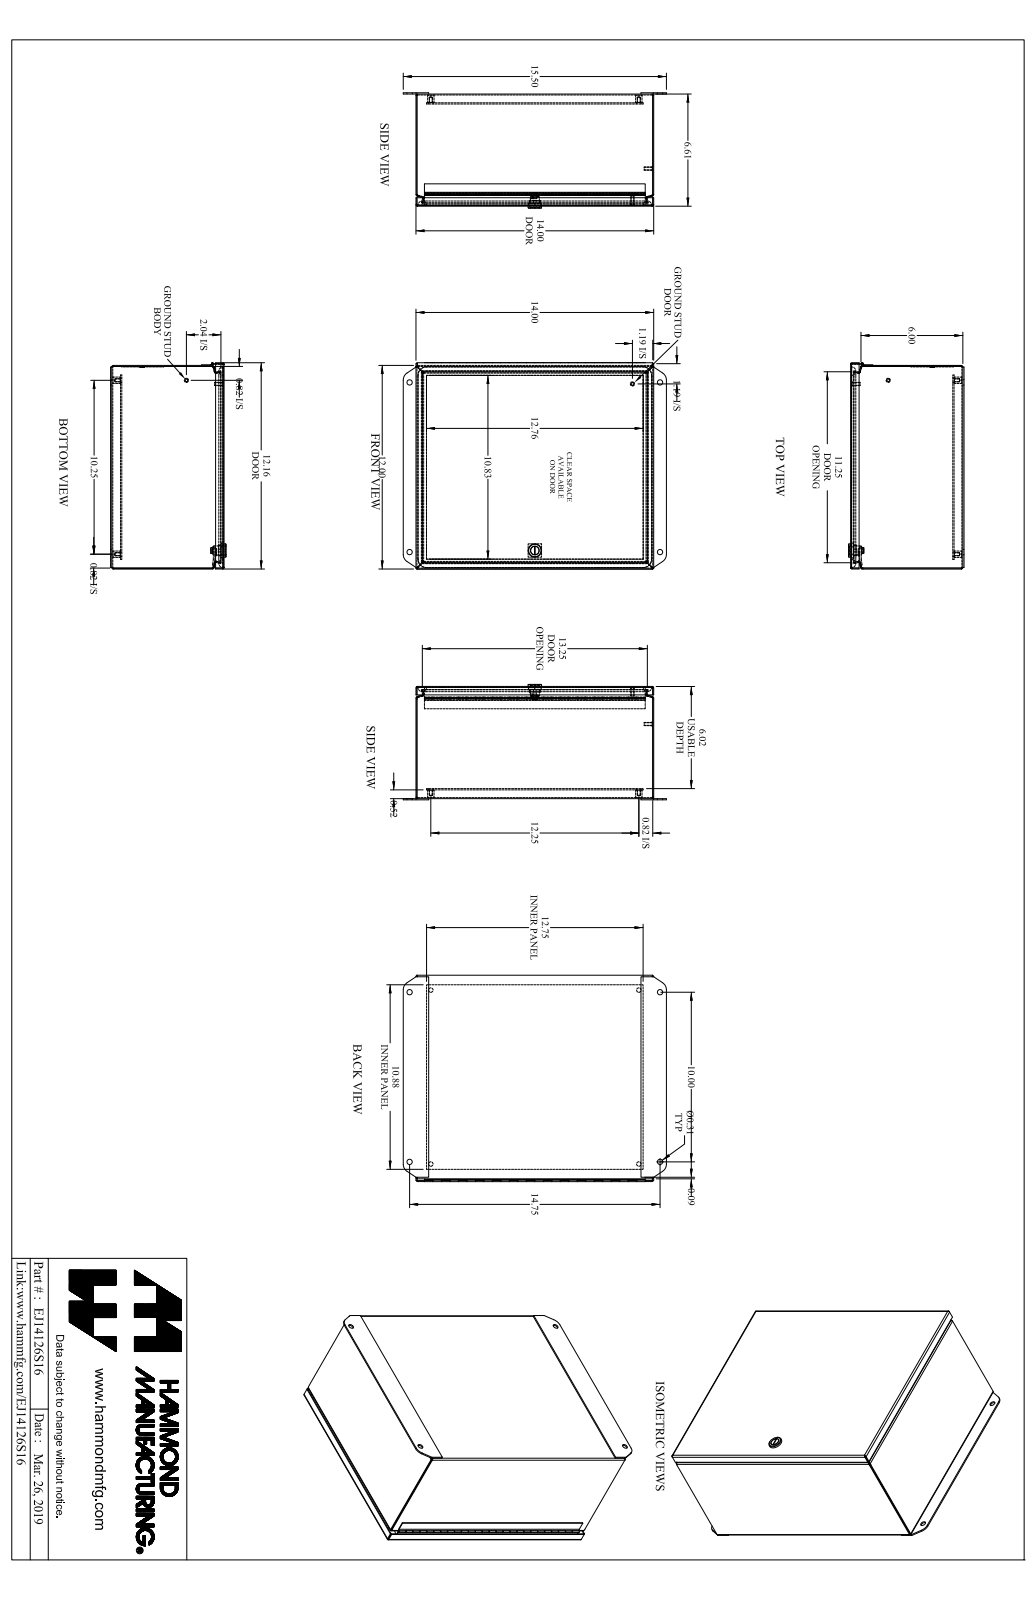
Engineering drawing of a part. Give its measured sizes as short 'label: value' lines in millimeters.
name: EJ14126S16_Default
written by: SolidWorks 2019 (CONFIG_CONTROL_DESIGN)
unit: mm
bodies: 16 solids, 660 faces (342 planar, 238 cylindrical, 80 other)
size: 393.7 × 309 × 172.8
volume: 953 700 mm³; area: 1 240 000 mm²
holes: 4× ⌀4, 4× ⌀6.7, 4× ⌀8, 1× ⌀1.3, 1× ⌀13.1
bosses: 4× ⌀9.5, 2× ⌀6.4, 2× ⌀4.8, 1× ⌀20, 1× ⌀13.6, 1× ⌀12.6, 1× ⌀11, 1× ⌀2.5
rounds: 16× R0.7, 16× R2.2, 12× R7.1, 4× R6.4, 4× R12.7, 4× R12.7, 2× R1.5, 1× R0.8
face distances: 1.4, 166.5, 1.8, 15, 167.9, 165, 303.4, 354.2, 154.8, 153.3
hole spacings: 31.9, 259.1, 342.9, 428.6, 155.7, 187.4, 254, 260.4
